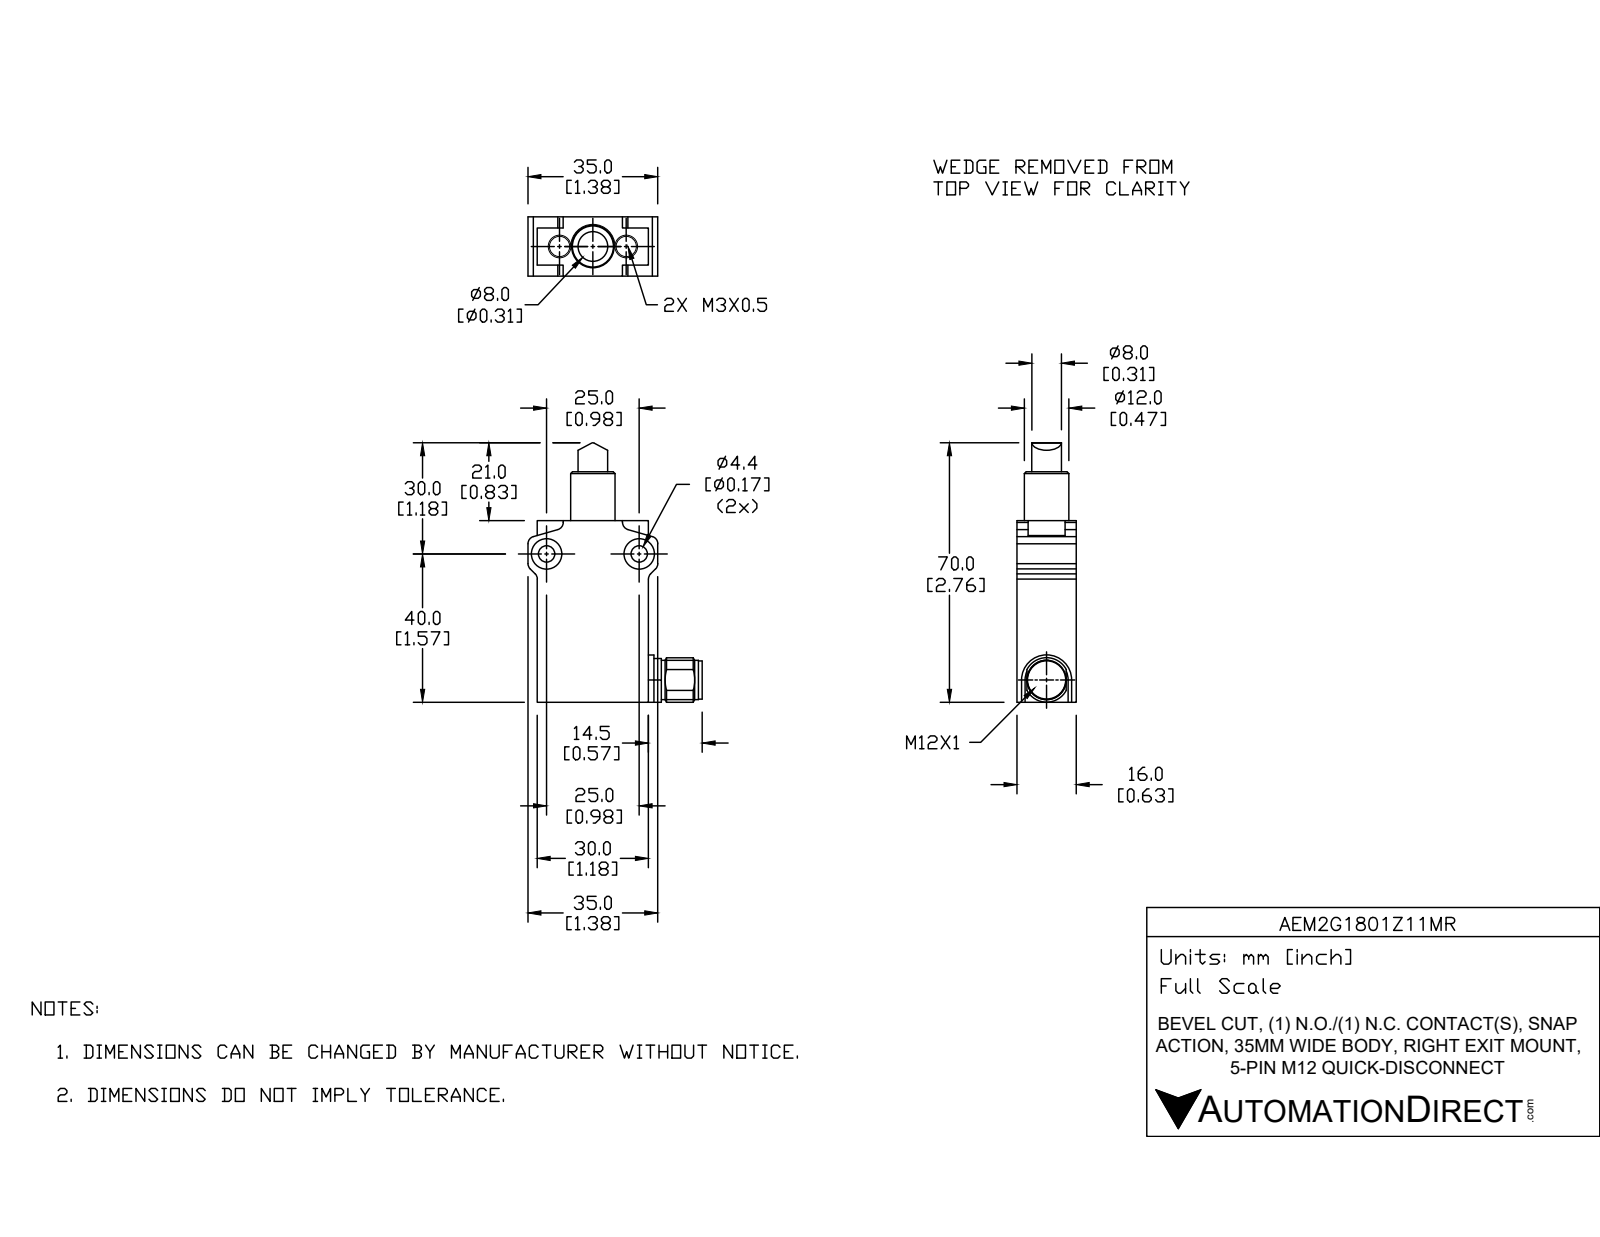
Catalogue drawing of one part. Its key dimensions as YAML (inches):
part_name: "AEM2G1801Z11MR"
step_written_by: "SolidWorks 2019 (AUTOMOTIVE_DESIGN)"
units: inches
bodies: {solids: 4, faces: 134, planar: 53, cylindrical: 48, other: 33}
overall_size: [2.874, 1.831, 0.63]
volume: 1.667
surface_area: 14.61
round_holes:
  - {diameter: 0.118, count: 2}
  - {diameter: 0.173, count: 2}
  - {diameter: 0.323, count: 2}
  - {diameter: 0.317, count: 1}
round_bosses_or_shafts:
  - {diameter: 0.472, count: 2}
  - {diameter: 0.417, count: 1}
  - {diameter: 0.406, count: 1}
  - {diameter: 0.315, count: 1}
partial_cylinders:
  - {radius: 0.079, count: 8}
  - {radius: 0.03, count: 1}
  - {radius: 0.256, count: 1}
face_to_face_distances: [0.63, 1.181, 2.047, 1.858, 0.189, 0.472, 0.098, 1.28, 0.157, 0.039]
hole_center_spacings: [0.374, 0.748, 0.984]
